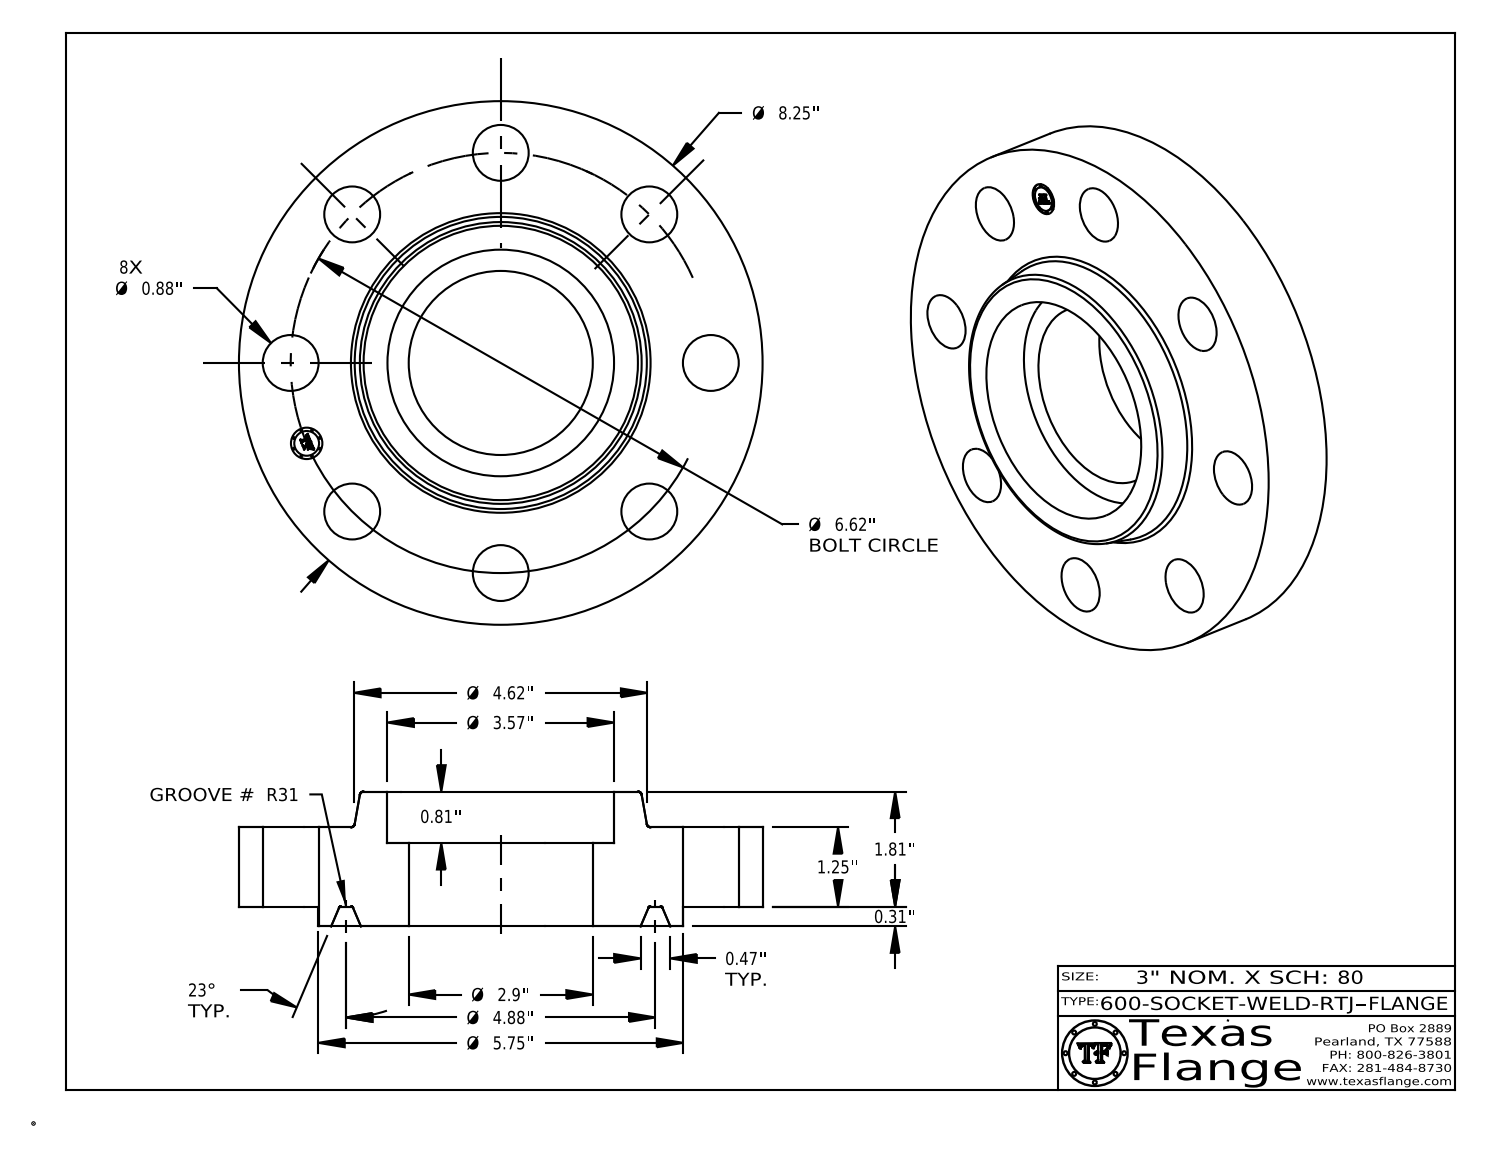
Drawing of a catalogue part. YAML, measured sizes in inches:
part_name: "600-SOCKET-WELD-RTJ"
step_written_by: "CATIA V5 STEP AP214 (AUTOMOTIVE_DESIGN)"
units: inches
bodies: {solids: 1, faces: 438, planar: 372, cylindrical: 52, other: 14}
overall_size: [8.25, 8.25, 2.123]
volume: 59.47
surface_area: 183.2
round_holes:
  - {diameter: 0.88, count: 8}
  - {diameter: 0.495, count: 1}
  - {diameter: 2.9, count: 1}
  - {diameter: 3.57, count: 1}
round_bosses_or_shafts:
  - {diameter: 0.03, count: 8}
  - {diameter: 8.25, count: 1}
  - {diameter: 5.75, count: 1}
  - {diameter: 0.39, count: 1}
face_to_face_distances: [1.25, 0.313, 1.563, 2.123, 1.81, 0.56, 1.313, 1, 0.25, 0.81]
hole_center_spacings: [3.31, 2.533, 6.116, 4.681, 4.681, 1.291, 3.678, 6.493]
